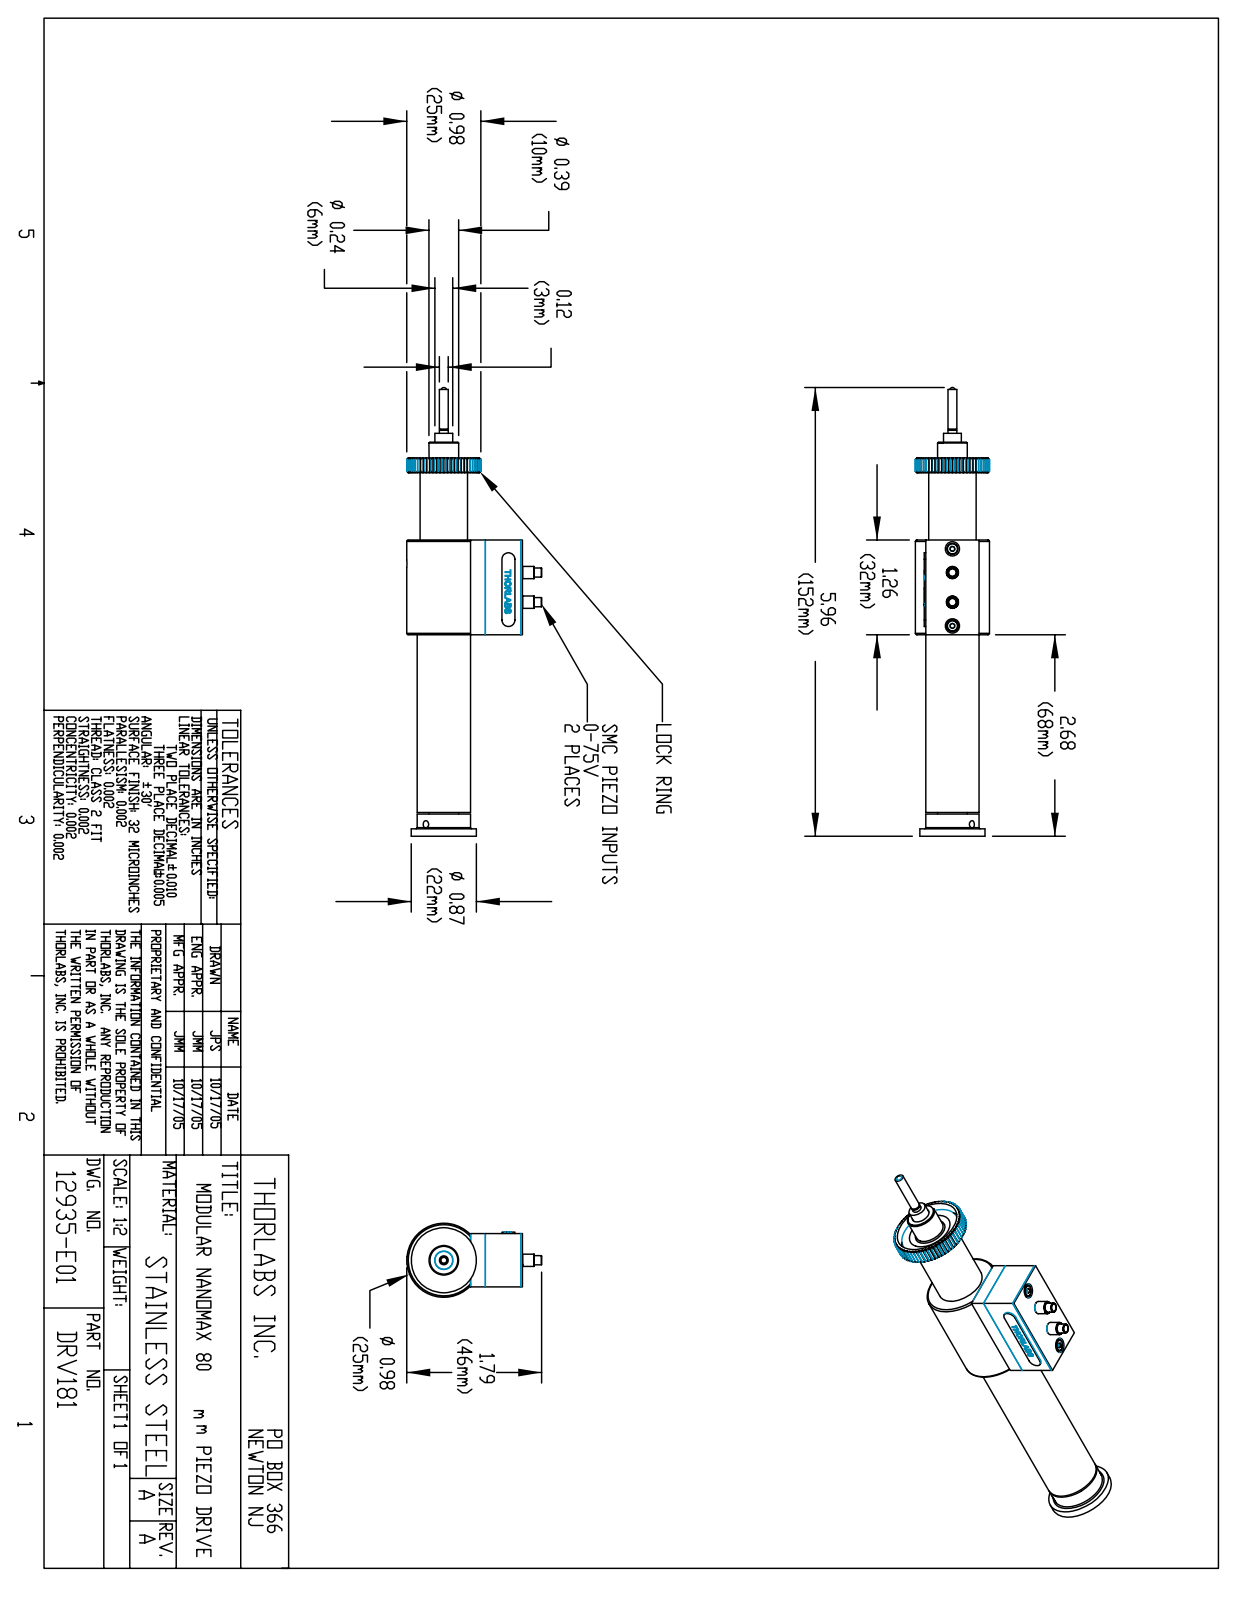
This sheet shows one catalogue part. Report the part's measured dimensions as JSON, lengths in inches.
{"part_name": "12935-E0W", "step_written_by": "SolidWorks 2007 (AUTOMOTIVE_DESIGN)", "units": "inches", "bodies": {"solids": 0, "faces": 467, "planar": 190, "cylindrical": 121, "other": 156}, "overall_size": [5.963, 1.792, 0.984], "round_holes": [[0.098, 4], [0.19, 2], [0.197, 2], [0.244, 1], [0.394, 1], [0.724, 1], [0.866, 1]], "round_bosses_or_shafts": [[0.163, 2], [0.15, 2], [0.122, 2], [0.709, 1], [0.63, 1], [0.236, 1], [0.118, 1], [0.091, 1]], "partial_cylinders_radius": [[0.087, 2], [0.492, 1]], "face_to_face_distances": [0.709, 0.689, 1.26, 2.677, 0.945, 2.205, 4.882, 3.937, 0.02, 4.941], "hole_center_spacings": [0.315, 0.709, 0.118, 0.197, 0.394, 0.512, 0.827, 1.024]}
